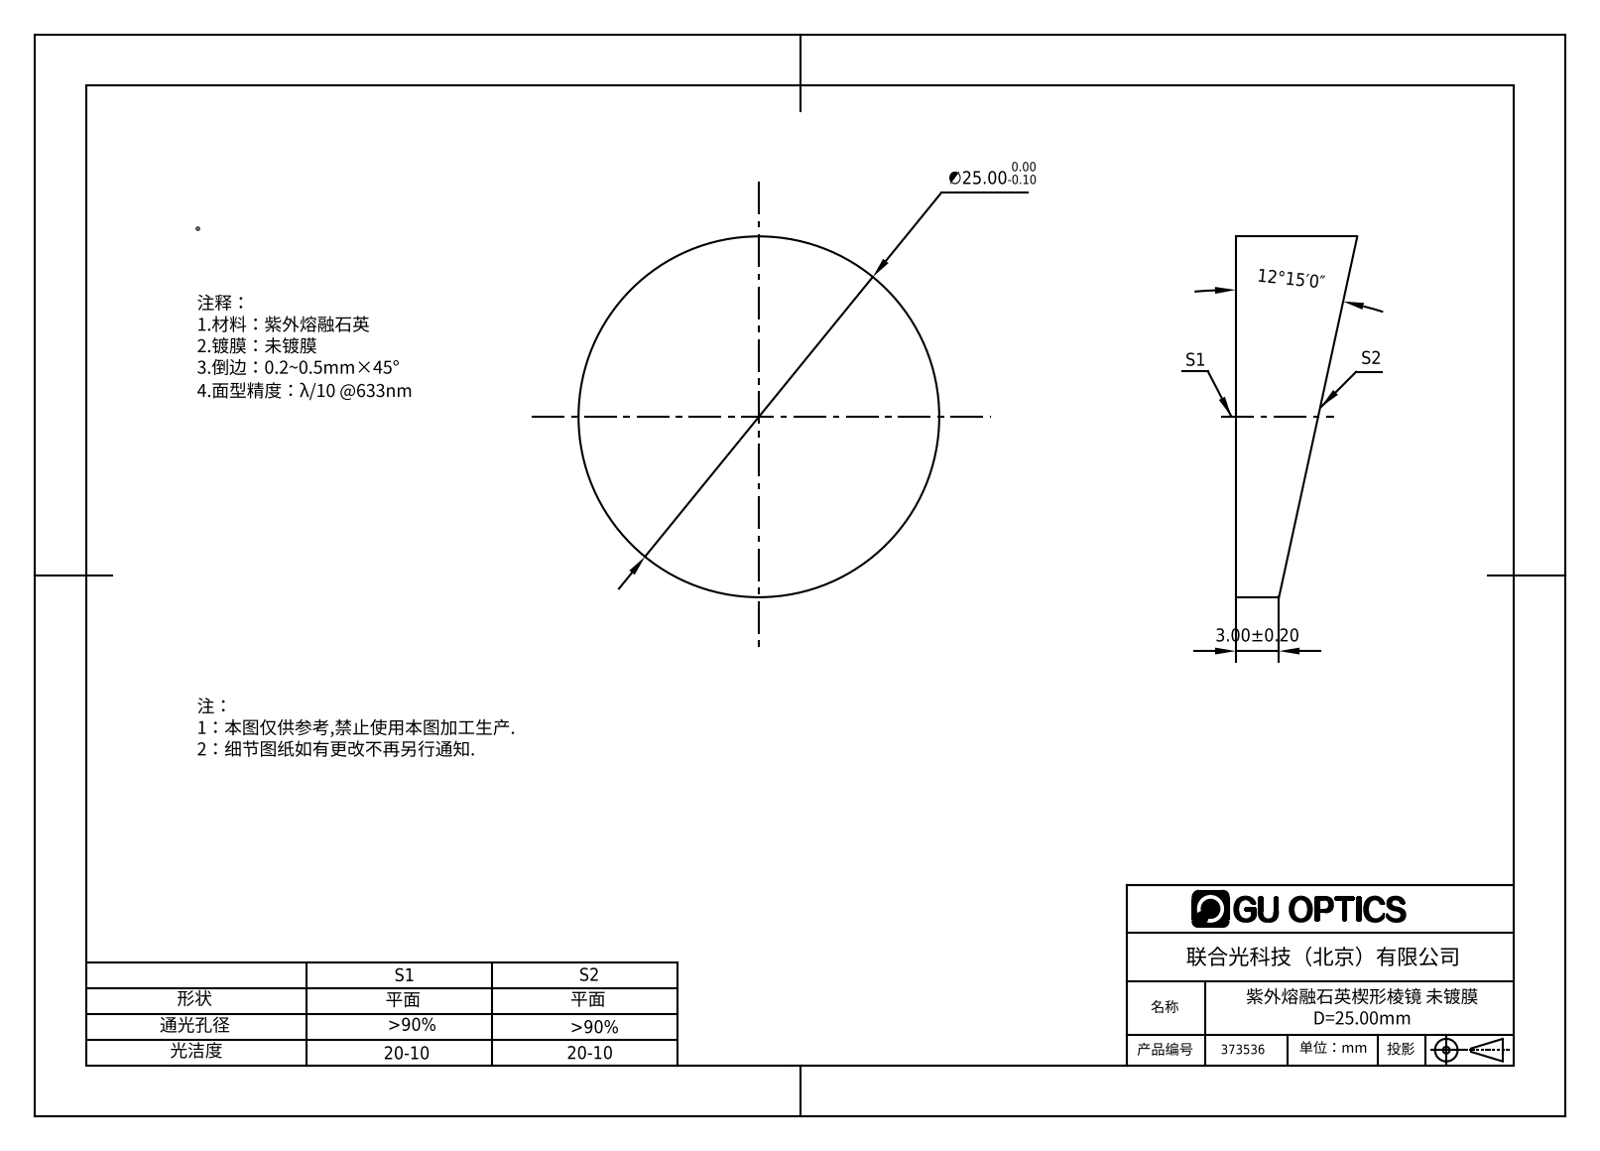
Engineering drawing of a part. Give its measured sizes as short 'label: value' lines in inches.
name: 373536
written by: SolidWorks 2016 (CONFIG_CONTROL_DESIGN)
unit: in
bodies: 1 solid, 4 faces (2 planar, 2 cylindrical, 0 other)
size: 0.984 × 0.984 × 0.332
volume: 0.171 in³; area: 2.235 in²
bosses: 1× ⌀0.984
